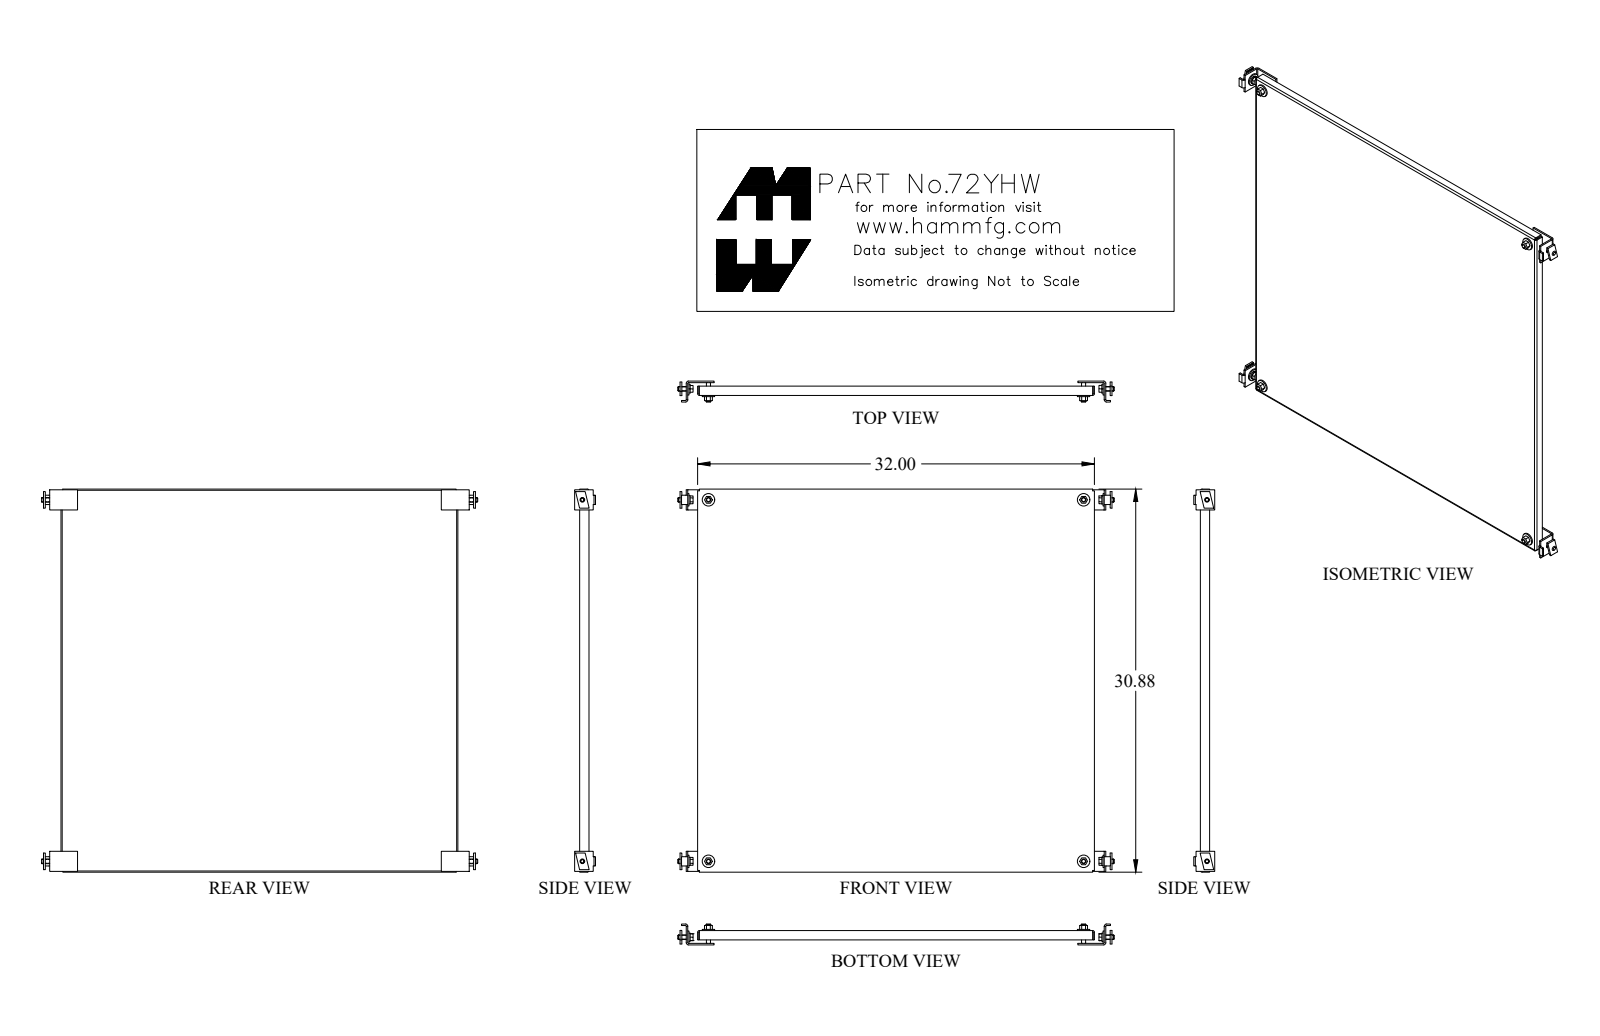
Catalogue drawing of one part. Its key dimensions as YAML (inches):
part_name: "72YHW_Default"
step_written_by: "SolidWorks 2018 (CONFIG_CONTROL_DESIGN)"
units: inches
bodies: {solids: 1, faces: 38, planar: 22, cylindrical: 16, other: 0}
overall_size: [32, 30.875, 0.75]
volume: 101
surface_area: 2140
round_holes:
  - {diameter: 0.563, count: 4}
partial_cylinders:
  - {radius: 0.048, count: 4}
  - {radius: 0.143, count: 4}
face_to_face_distances: [0.095, 30.78, 31.905, 30.685, 30.875, 32, 31.81, 0.75, 0.655, 0.143]
hole_center_spacings: [29.125, 30.25, 41.993]
